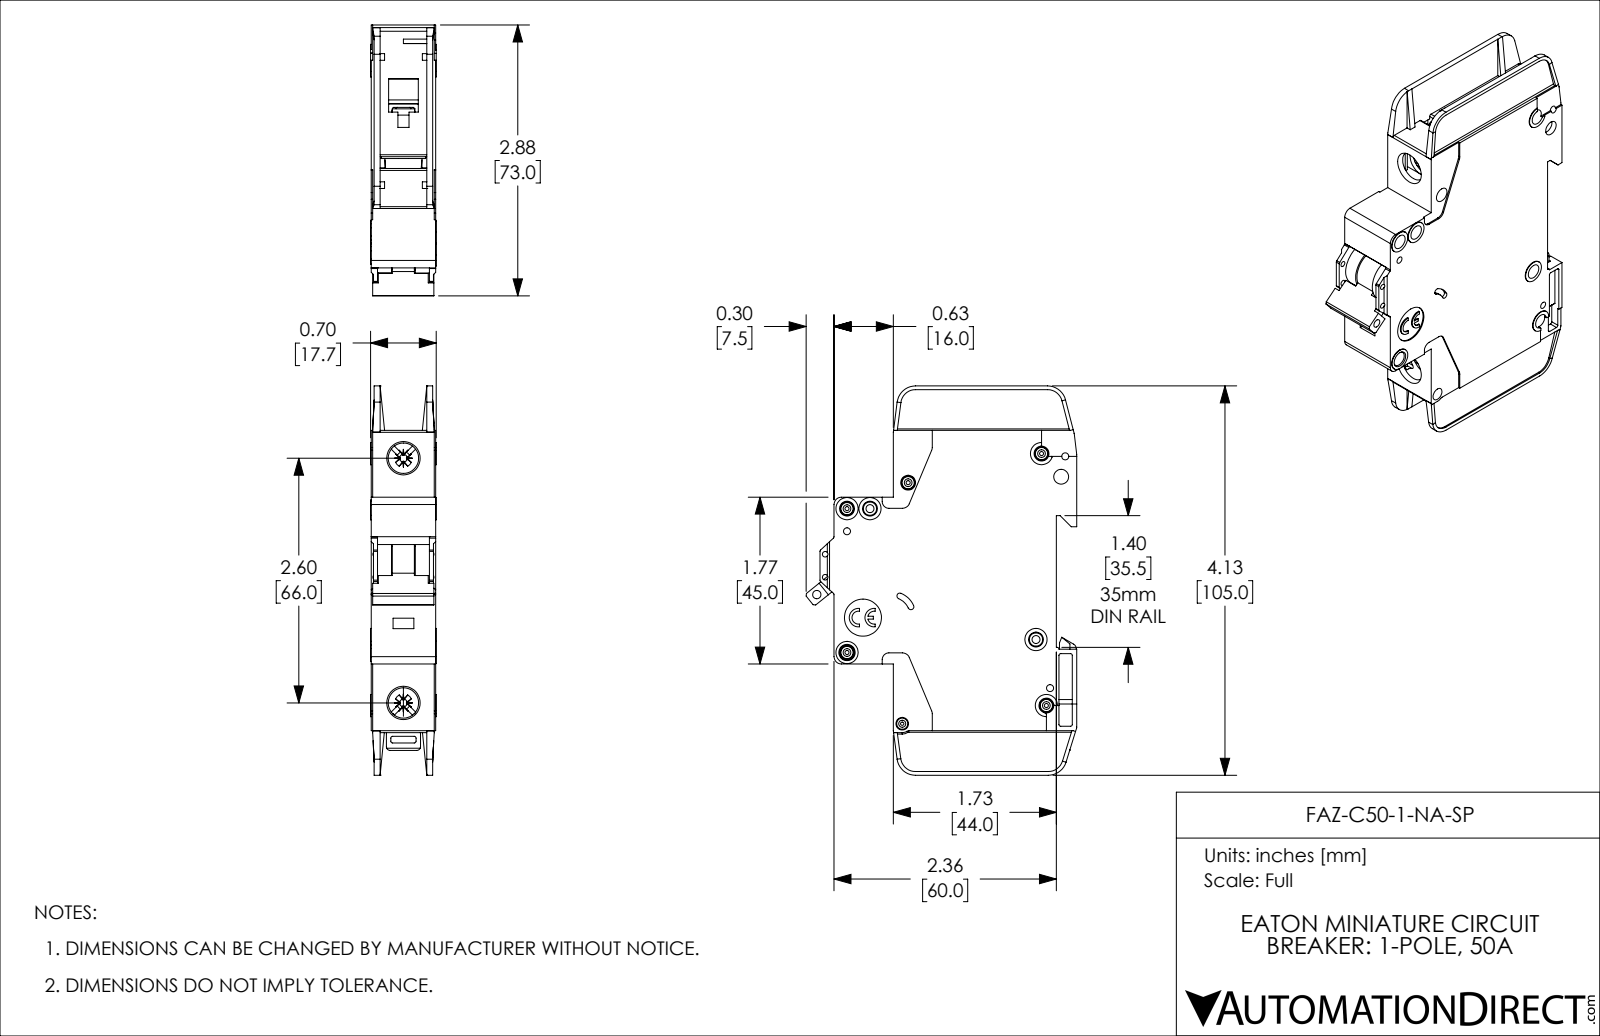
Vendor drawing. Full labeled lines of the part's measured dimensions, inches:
Part name (STEP PRODUCT): FAZ-C50-1-NA-SP
STEP written by: SolidWorks 2019 (AUTOMOTIVE_DESIGN)
Units: inches
Bodies: 1 solid, 1127 faces (671 planar, 357 cylindrical, 99 other)
Overall size (bounding box): 4.134 × 2.876 × 0.697
Volume: 4.682 in³ · Surface area: 41.01 in²
Round holes (diameter × count): ⌀0.157 ×8, ⌀0.043 ×5, ⌀0.075 ×4, ⌀0.059 ×2, ⌀0.085 ×2, ⌀0.323 ×2, ⌀0.035 ×1, ⌀0.089 ×1, ⌀0.098 ×1, ⌀0.134 ×1, ⌀0.394 ×1
Round bosses / shafts (diameter × count): ⌀0.13 ×5, ⌀0.236 ×4, ⌀0.118 ×2, ⌀0.098 ×1
Partial cylindrical surfaces — rounded edges, fillets, slot ends (radius × count): R0.02 ×42, R0.016 ×10, R0.039 ×10, R0.079 ×8, R0.197 ×5, R0.008 ×4, R0.026 ×4, R0.043 ×4
Main face-to-face distances: 0.047, 0.685, 0.591, 0.638, 0.094, 0.543, 0.016, 0.031, 0.496, 0.575
Hole centre spacings: 0.244, 0.537, 0.87, 0.189, 0.199, 0.204, 0.221, 0.24
